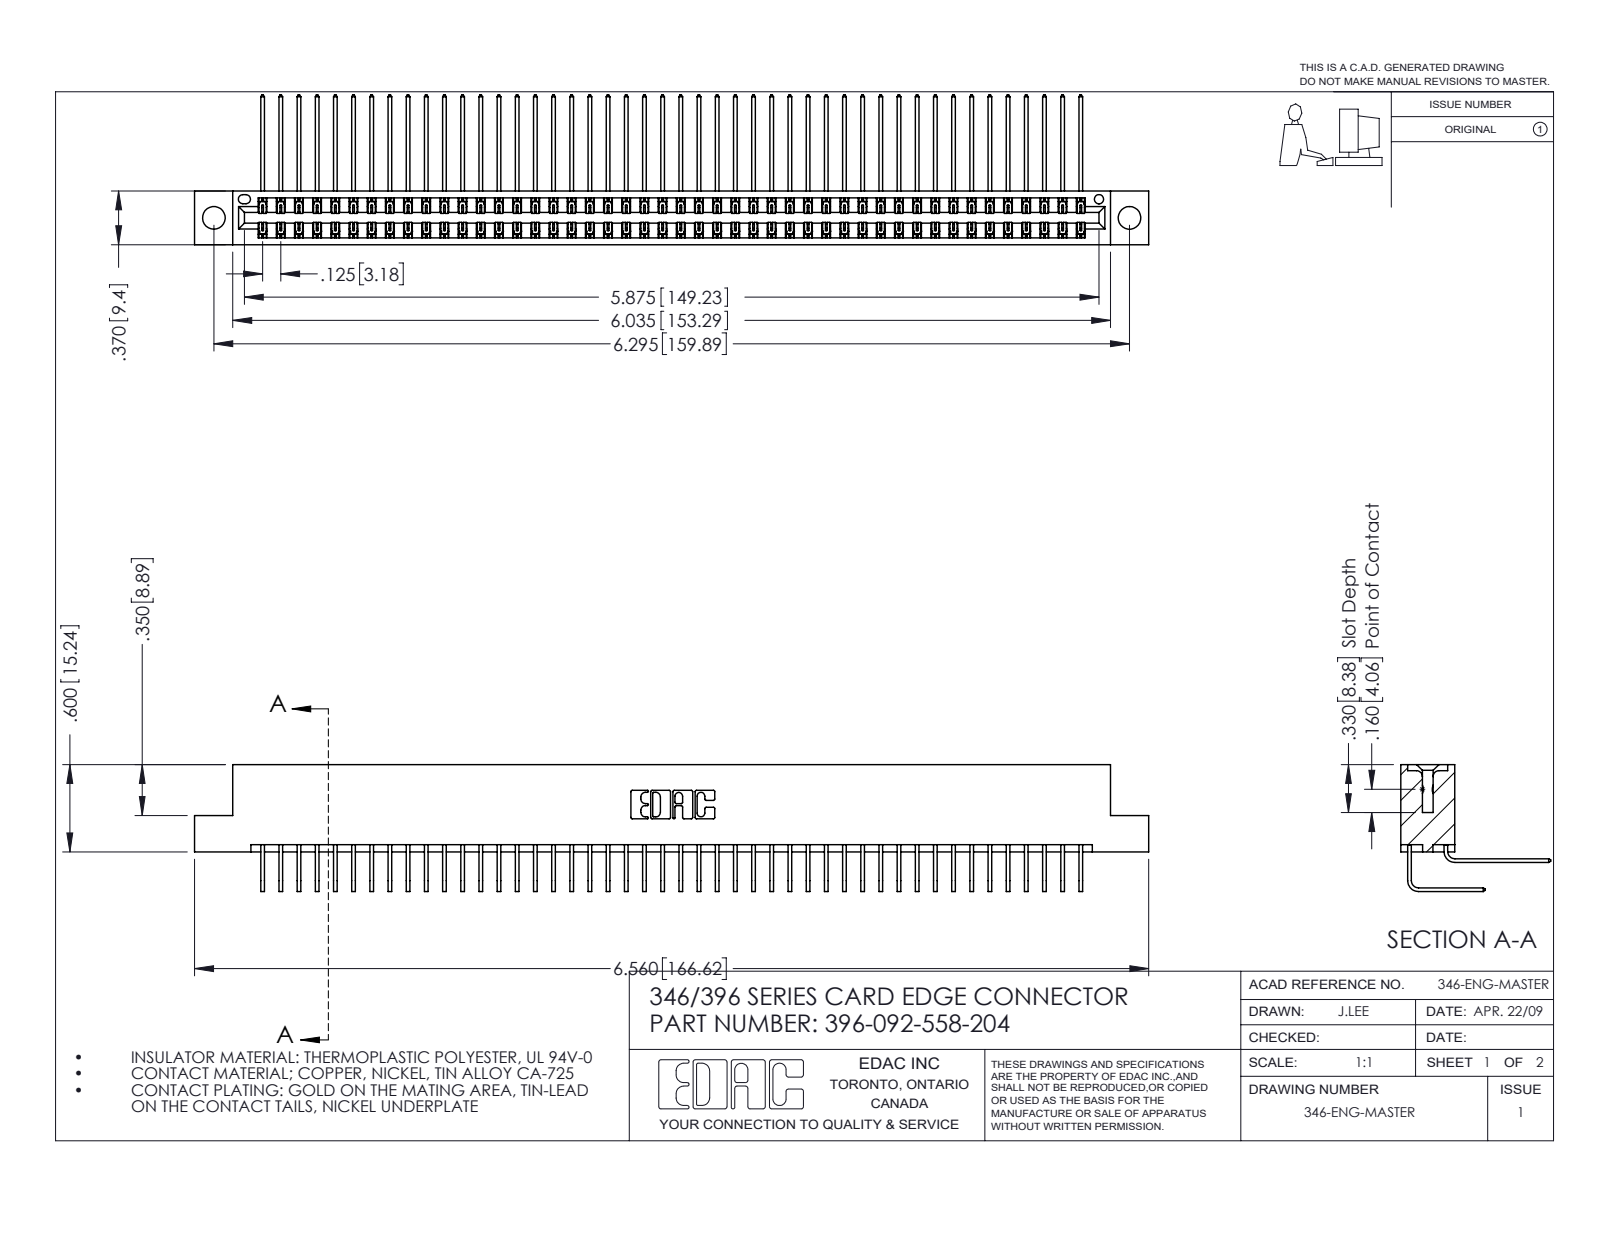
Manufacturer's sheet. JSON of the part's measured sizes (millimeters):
{"part_name": "346 Part_Flush Mounting Lugs - 0.156 Dia-TH; 345-292-001_558 559 Tail - 1; 345-292-001_558 Tail - 2; 396-092-558-204", "step_written_by": "SolidWorks 2016 (CONFIG_CONTROL_DESIGN)", "units": "millimeters", "bodies": {"solids": 93, "faces": 5090, "planar": 3480, "cylindrical": 1610, "other": 0}, "overall_size": [166.6, 26.2, 22.2], "volume_mm3": 16710, "surface_area_mm2": 25410, "round_holes": [[4, 2], [1.6, 1]], "partial_cylinders_radius": [[0.2, 138], [0.3, 22], [0.2, 6], [0.8, 6], [0.7, 3], [0.4, 2], [0.6, 2], [0.6, 2]], "face_to_face_distances": [8.2, 1.2, 0.6, 9.4, 6.4, 7.6, 1.8, 7, 3.8, 5.6], "hole_center_spacings": [6.2, 154.6, 159.9]}
